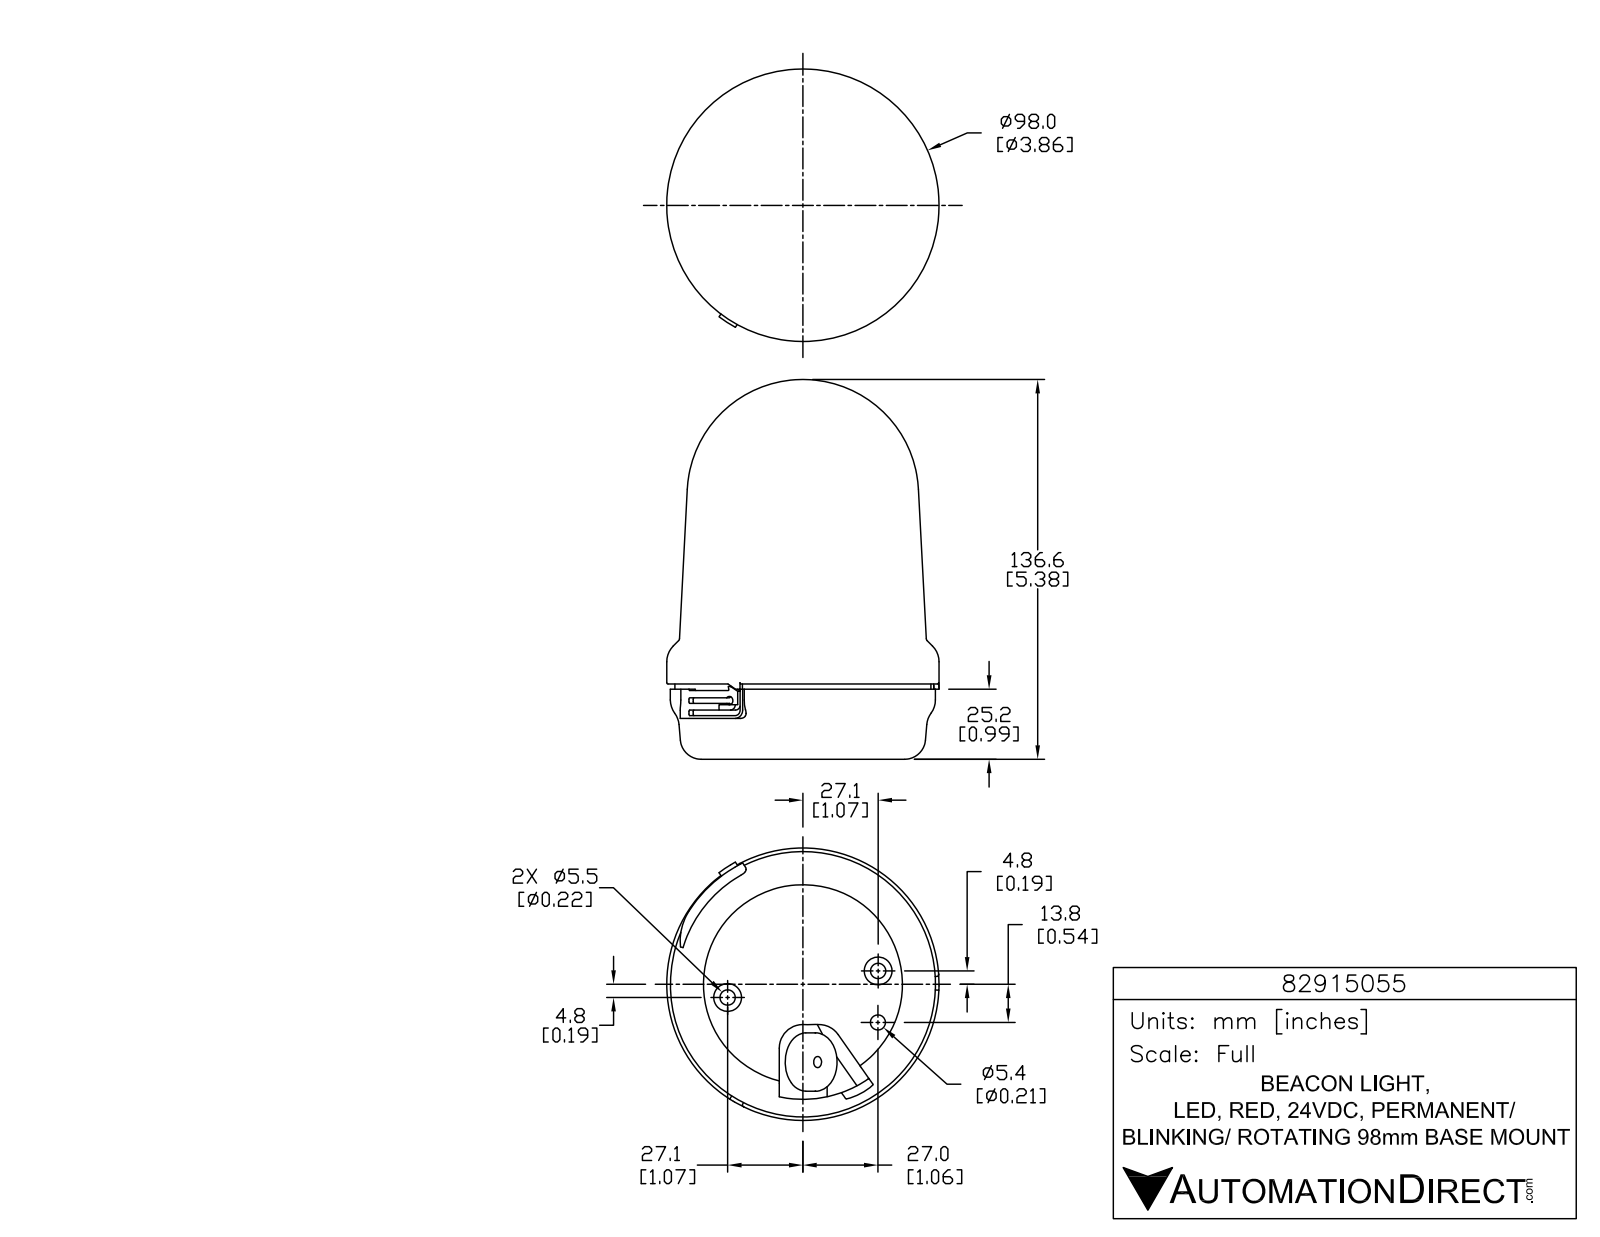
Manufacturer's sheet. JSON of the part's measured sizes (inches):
{"part_name": "82915055", "step_written_by": "SolidWorks 2015 (AUTOMOTIVE_DESIGN)", "units": "inches", "bodies": {"solids": 1, "faces": 872, "planar": 566, "cylindrical": 204, "other": 102}, "overall_size": [5.378, 3.858, 3.858], "volume_in3": 44.69, "surface_area_in2": 73.66, "round_holes": [[0.059, 3], [0.217, 2], [0.157, 1], [0.213, 1], [2.819, 1]], "round_bosses_or_shafts": [[0.339, 3], [0.084, 3], [0.394, 2], [3.858, 1], [3.756, 1], [3.626, 1], [0.827, 1]], "partial_cylinders_radius": [[0.005, 9], [0.005, 6], [0.012, 6], [0.012, 6], [0.012, 6], [0.196, 6], [0.02, 5], [0.039, 4]], "face_to_face_distances": [1.045, 0.972, 0.073, 0.02, 0.992, 1.065, 0.236, 0.579, 0.559, 0.413], "hole_center_spacings": [1.083, 0.73, 1.193, 2.158, 2.165]}
